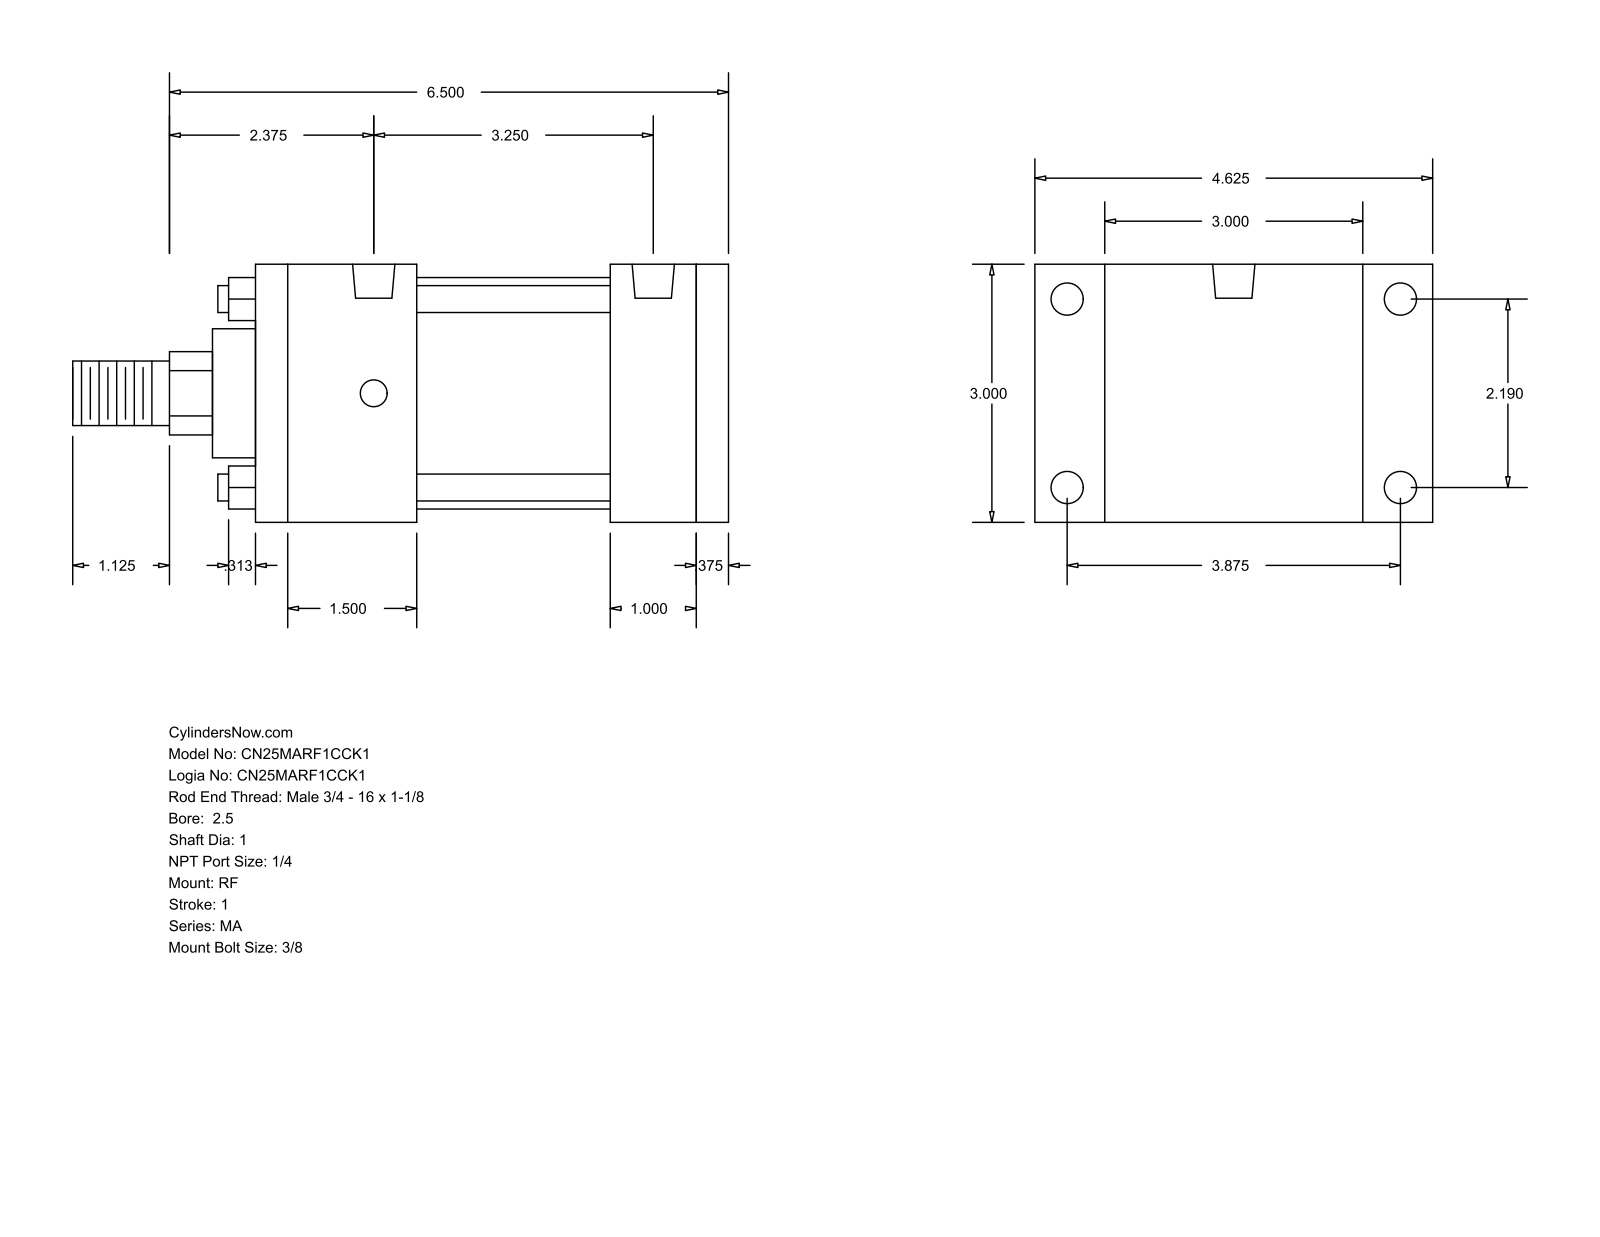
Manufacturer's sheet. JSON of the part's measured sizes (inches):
{"part_name": "MA_RF__0250_1", "step_written_by": "GSSL Pune (CONFIG_CONTROL_DESIGN)", "units": "inches", "bodies": {"solids": 0, "faces": 92, "planar": 64, "cylindrical": 28, "other": 0}, "overall_size": [7.625, 4.625, 3], "round_holes": [[0.313, 4], [0.375, 4], [0.492, 2]], "round_bosses_or_shafts": [[0.313, 4], [2.69, 1], [1.5, 1], [1, 1], [0.75, 1]], "partial_cylinders_radius": [[0.484, 1]], "face_to_face_distances": [3, 5.5, 0.375, 5.125, 1.875, 4.125, 2.25, 3.25, 3.625, 1], "hole_center_spacings": [2.19, 3.25, 3.875, 4.451]}
